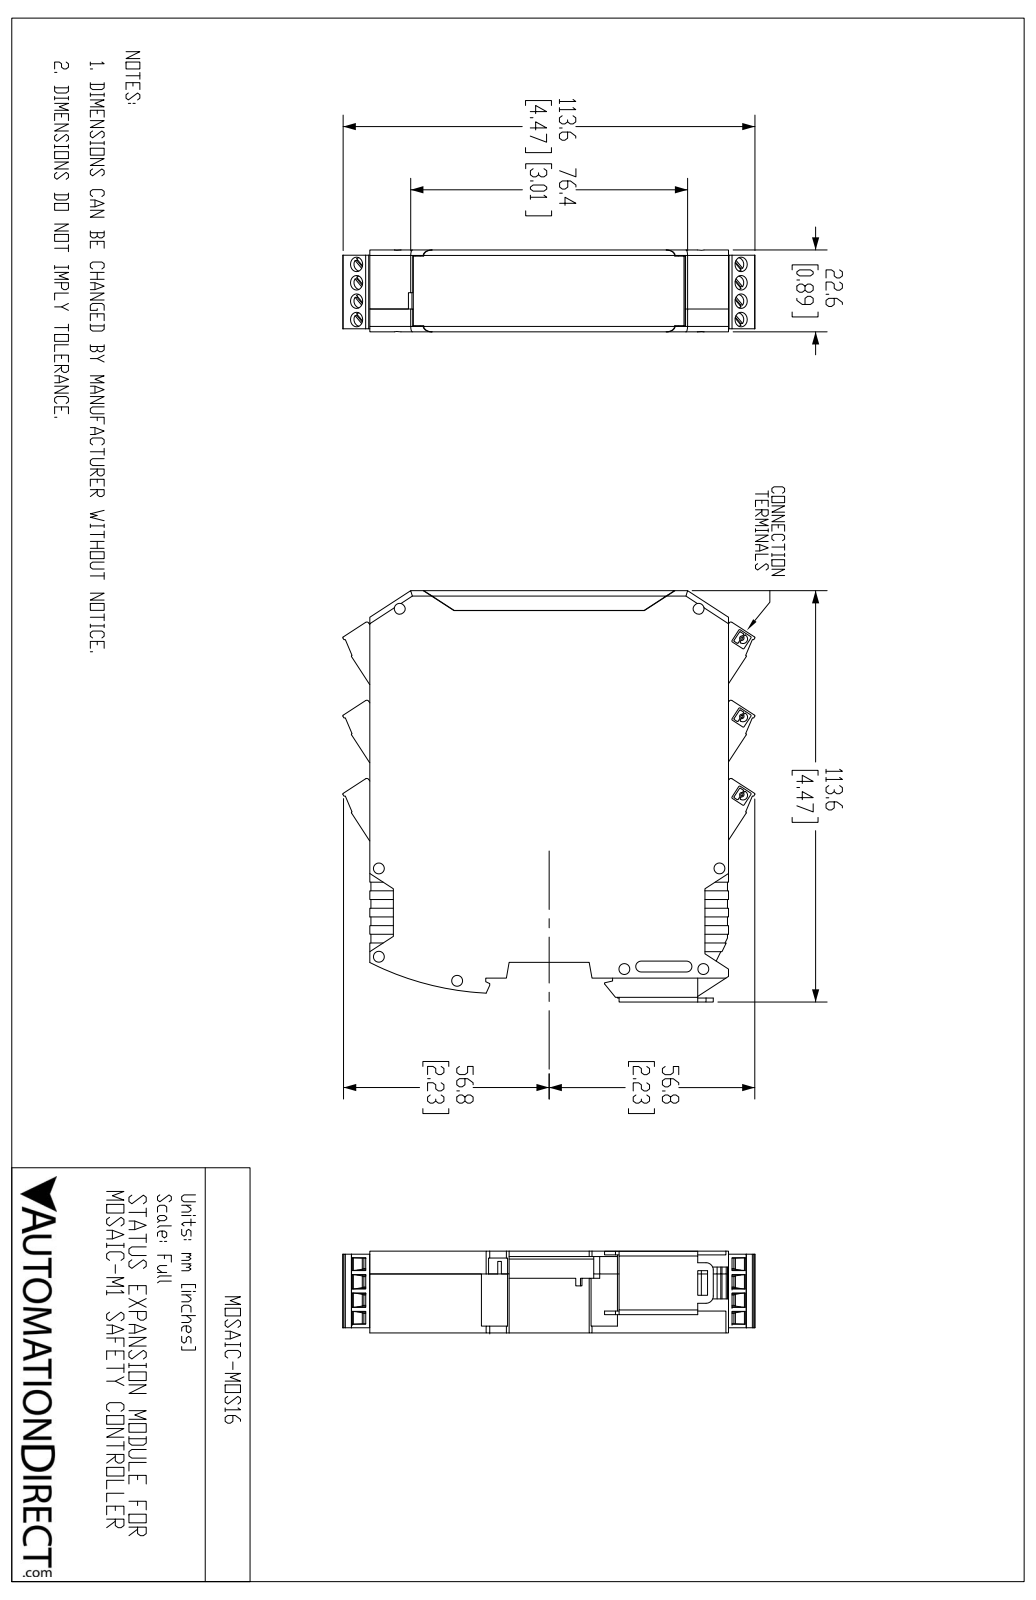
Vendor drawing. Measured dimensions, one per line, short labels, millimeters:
name: MOSAIC-MI16
written by: SolidWorks 2017 (AUTOMOTIVE_DESIGN)
unit: mm
bodies: 13 solids, 2249 faces (1787 planar, 411 cylindrical, 51 other)
size: 113.7 × 113.6 × 22.6
volume: 70 140 mm³; area: 86 320 mm²
holes: 24× ⌀4, 18× ⌀2.8, 14× ⌀1.4, 14× ⌀3, 1× ⌀1.6
bosses: 24× ⌀3.8, 6× ⌀0.6, 1× ⌀4.5, 1× ⌀2.8, 1× ⌀1.3
rounds: 60× R0.2, 24× R0.2, 24× R0.3, 24× R0.7, 24× R2.9, 19× R0.3, 18× R0.8, 8× R1.5
face distances: 1.2, 21.4, 22.6, 20.1, 18.1, 0.8, 1, 67.8, 1.6, 67.8
hole spacings: 5.1, 12.8, 18.8, 10.2, 11.8, 15.5, 18.1, 24.1
